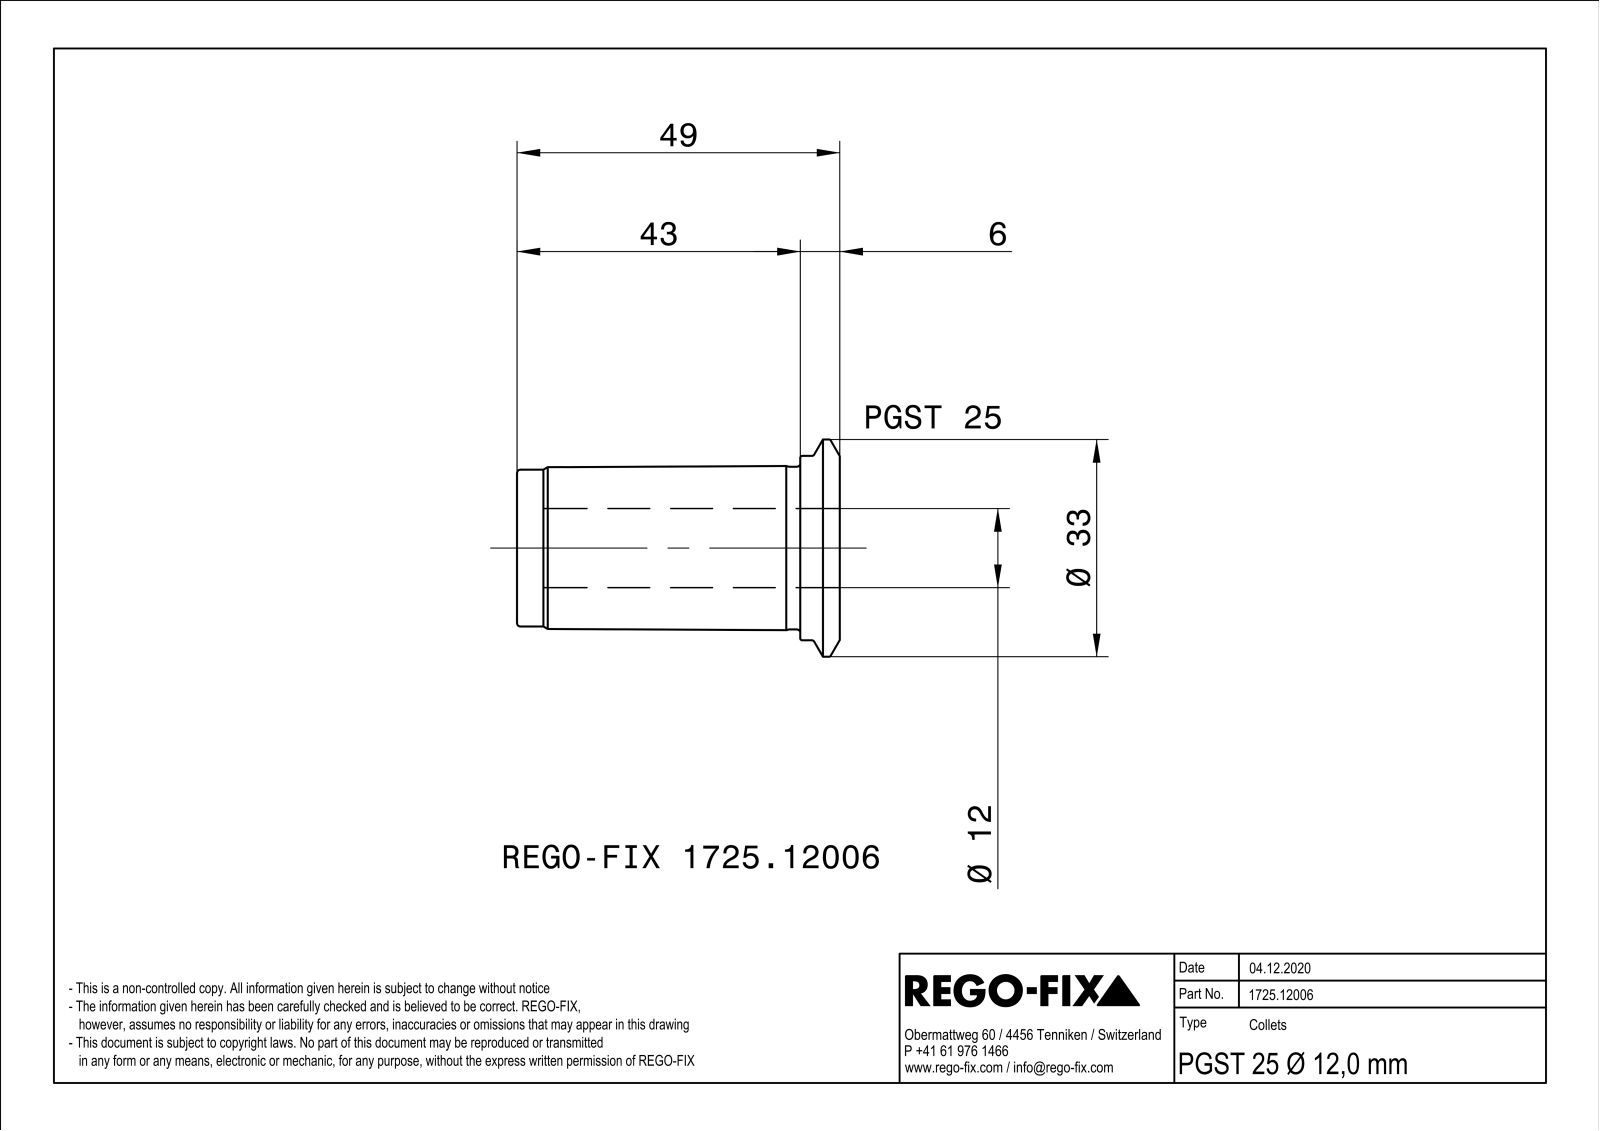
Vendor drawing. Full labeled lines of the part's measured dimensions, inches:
Part name (STEP PRODUCT): NOCUT
STEP written by: SIEMENS PLM Software Solid Edge ST10 (AUTOMOTIVE_DESIGN)
Units: inches
Bodies: 2 solids, 41 faces (7 planar, 13 cylindrical, 21 other)
Overall size (bounding box): 1.929 × 1.298 × 1.298
Volume: 1.196 in³ · Surface area: 12.98 in²
Round holes (diameter × count): ⌀0.118 ×3, ⌀0.197 ×1, ⌀0.472 ×1, ⌀0.834 ×1, ⌀0.878 ×1
Round bosses / shafts (diameter × count): ⌀1.298 ×1, ⌀1.102 ×1, ⌀0.972 ×1, ⌀0.937 ×1, ⌀0.866 ×1, ⌀0.827 ×1
Main face-to-face distances: 1.713, 1.929, 0.217, 1.732, 0.02, 0.197, 0.236, 1.476, 1.496, 1.693
Hole centre spacings: 0.236, 0.409, 0.409
